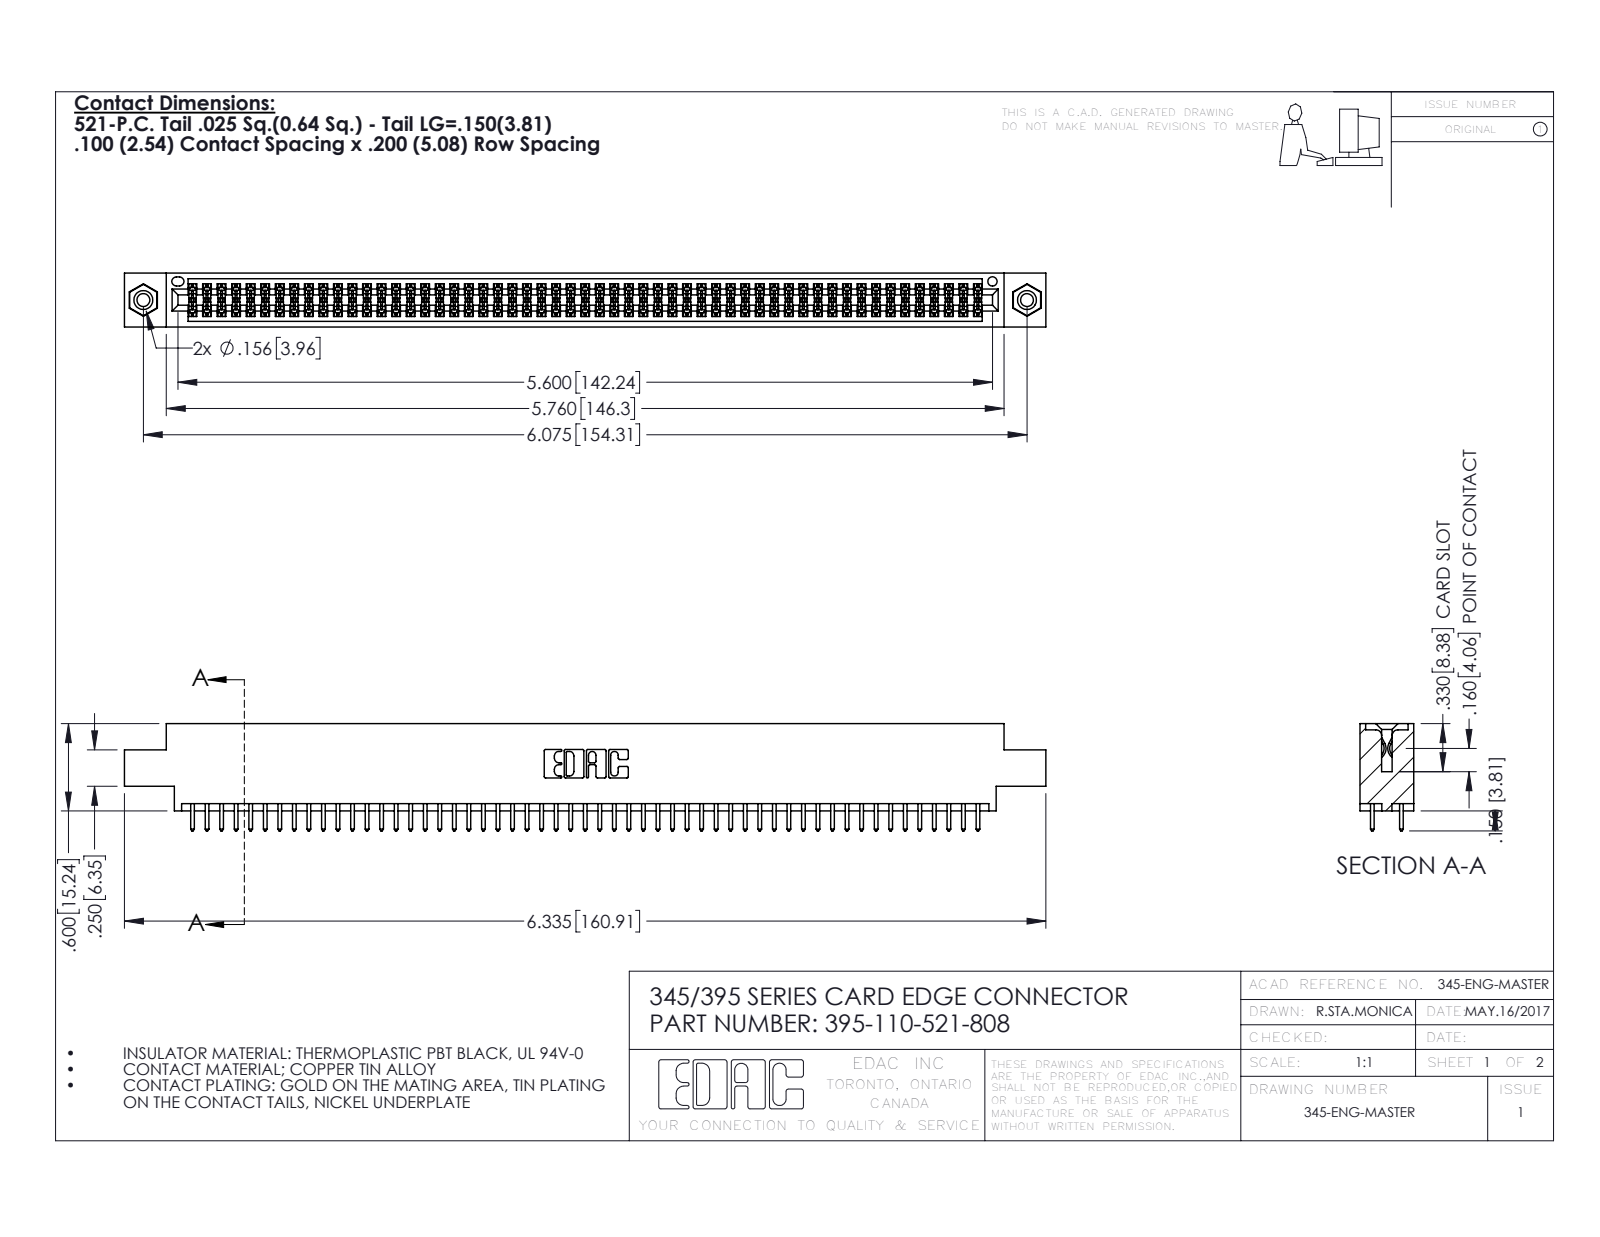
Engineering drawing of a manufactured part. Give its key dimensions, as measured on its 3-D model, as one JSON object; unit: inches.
{"part_name": "345-292-001_345-293-121; 345 Part_0.170 Offset - 0.156 Dia-TI; 345-250-001_345-250-003-102; 395-110-521-808", "step_written_by": "SolidWorks 2016 (CONFIG_CONTROL_DESIGN)", "units": "inches", "bodies": {"solids": 113, "faces": 5690, "planar": 3746, "cylindrical": 1928, "other": 16}, "overall_size": [6.335, 0.737, 0.37], "volume_in3": 0.951, "surface_area_in2": 35.89, "round_holes": [[0.089, 2], [0.125, 2], [0.156, 2], [0.064, 1]], "round_bosses_or_shafts": [[0.155, 2]], "partial_cylinders_radius": [[0.006, 165], [0.01, 110], [0.01, 22], [0.007, 6], [0.031, 6], [0.026, 3], [0.014, 2], [0.019, 2]], "face_to_face_distances": [0.072, 0.298, 0.2, 0.37, 0.098, 0.272, 0.025, 0.225, 0.175, 0.149], "hole_center_spacings": [0.27, 5.839, 6.075]}
